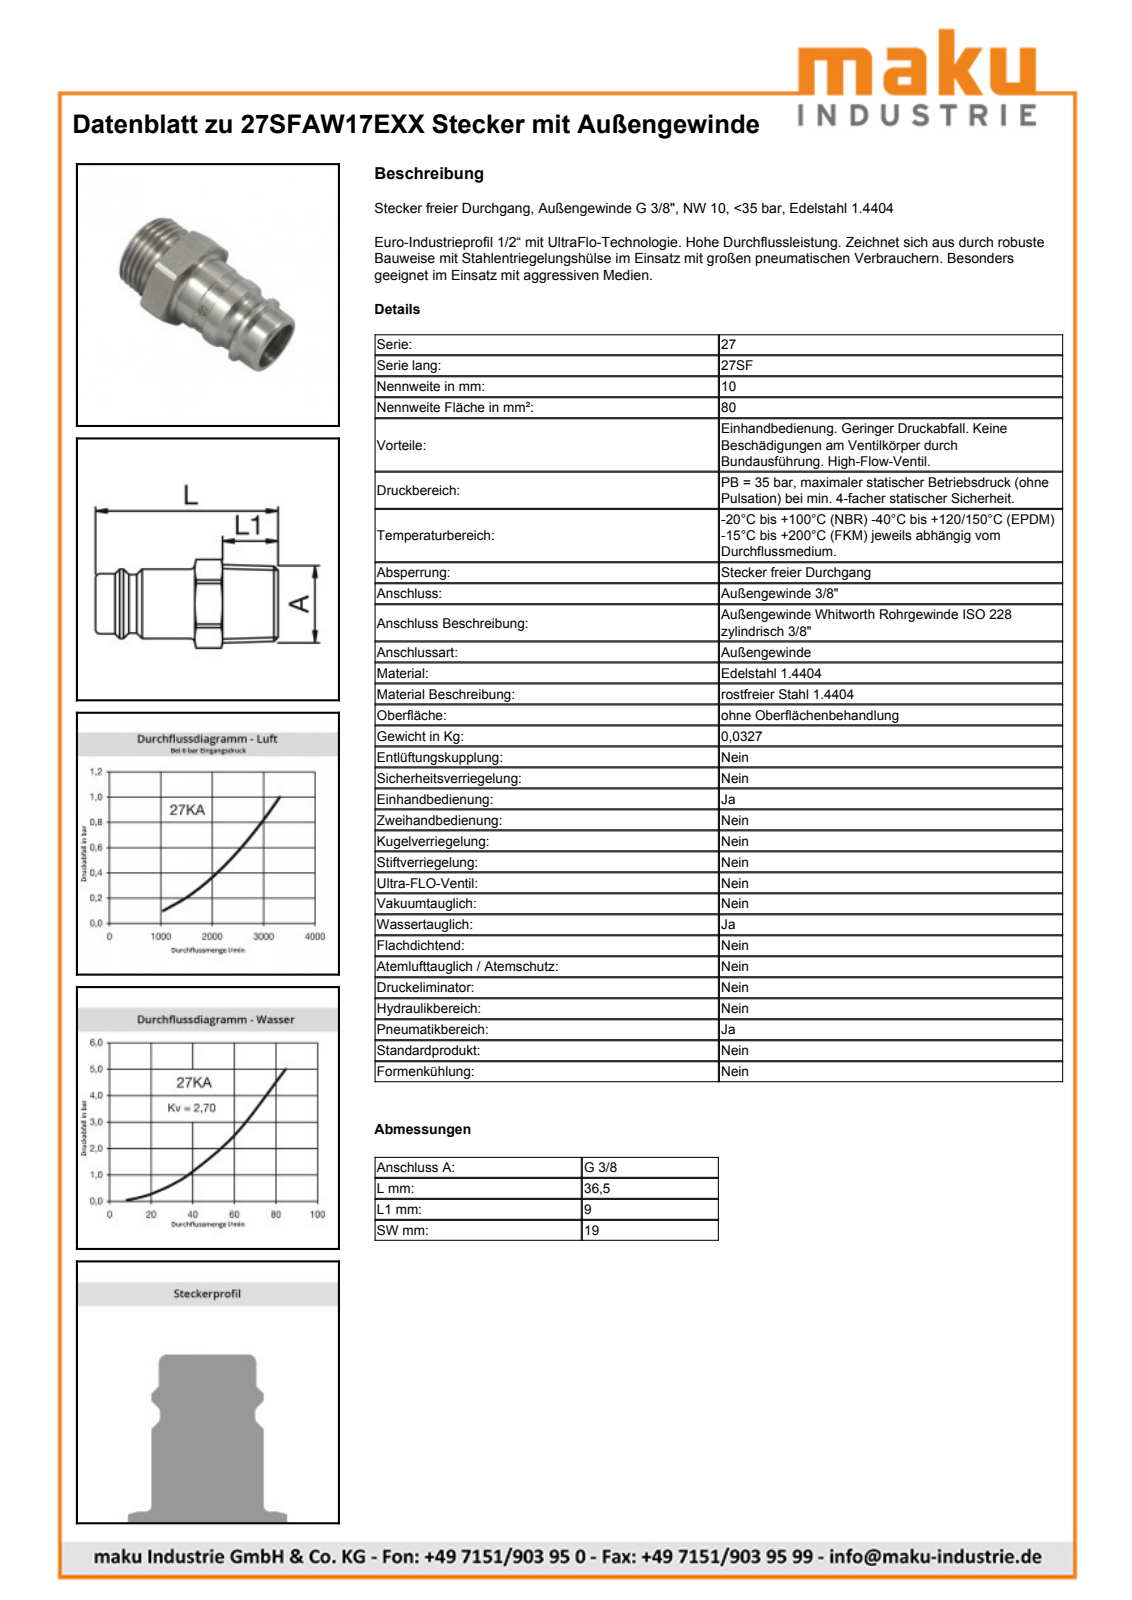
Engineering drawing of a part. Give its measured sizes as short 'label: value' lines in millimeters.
name: D105964
written by: Autodesk Inventor 2011 (AUTOMOTIVE_DESIGN)
unit: mm
bodies: 1 solid, 230 faces (95 planar, 36 cylindrical, 99 other)
size: 36.5 × 21.4 × 19
volume: 4 266 mm³; area: 3 413 mm²
holes: 1× ⌀10
bosses: 1× ⌀16.66, 1× ⌀15, 1× ⌀14.5, 1× ⌀13, 1× ⌀12.65
rounds: 1× R7.15, 1× R10.7
face distances: 19, 9, 6, 15, 21.5, 27.5, 36.5, 15.7, 5.8, 11.8
